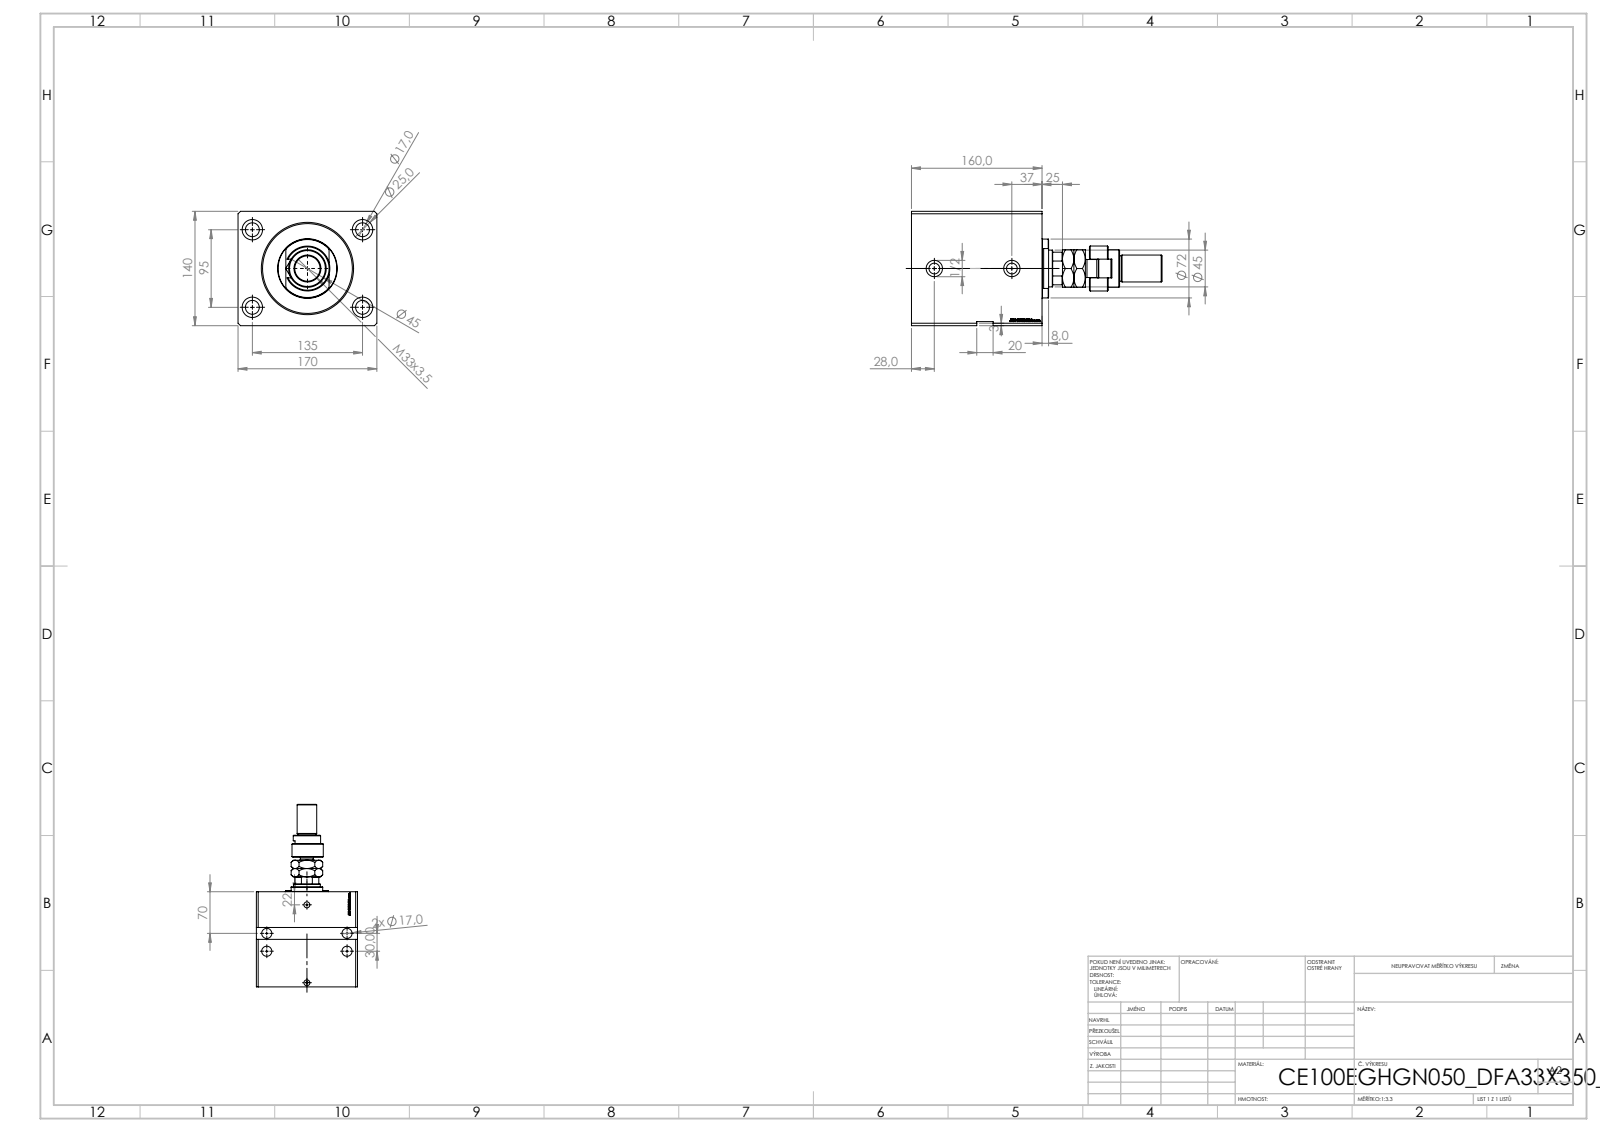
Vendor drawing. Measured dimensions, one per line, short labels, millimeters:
name: FEMALE_PART_FOR_DFA; V250CE_C_VCP; V250CE_VC_E; MFA (+1 more)
written by: SolidWorks 2019 (CONFIG_CONTROL_DESIGN)
unit: mm
bodies: 5 solids, 1038 faces (499 planar, 109 cylindrical, 430 other)
size: 307 × 170 × 140
volume: 3 374 000 mm³; area: 359 466 mm²
holes: 8× ⌀17, 4× ⌀1.25, 4× ⌀25, 2× ⌀10, 2× ⌀13.16, 2× ⌀20, 1× ⌀31.5, 1× ⌀39, 1× ⌀45, 1× ⌀100, 1× ⌀113
bosses: 1× ⌀72, 1× ⌀55, 1× ⌀46, 1× ⌀35, 1× ⌀33, 1× ⌀31, 1× ⌀22
rounds: 1× R11.5, 1× R22
face distances: 140, 170, 160, 28.9, 131.1, 25, 135, 106.1, 50, 85
hole spacings: 82.54, 135, 95, 30, 82.83, 85.49, 85.82, 103.15
